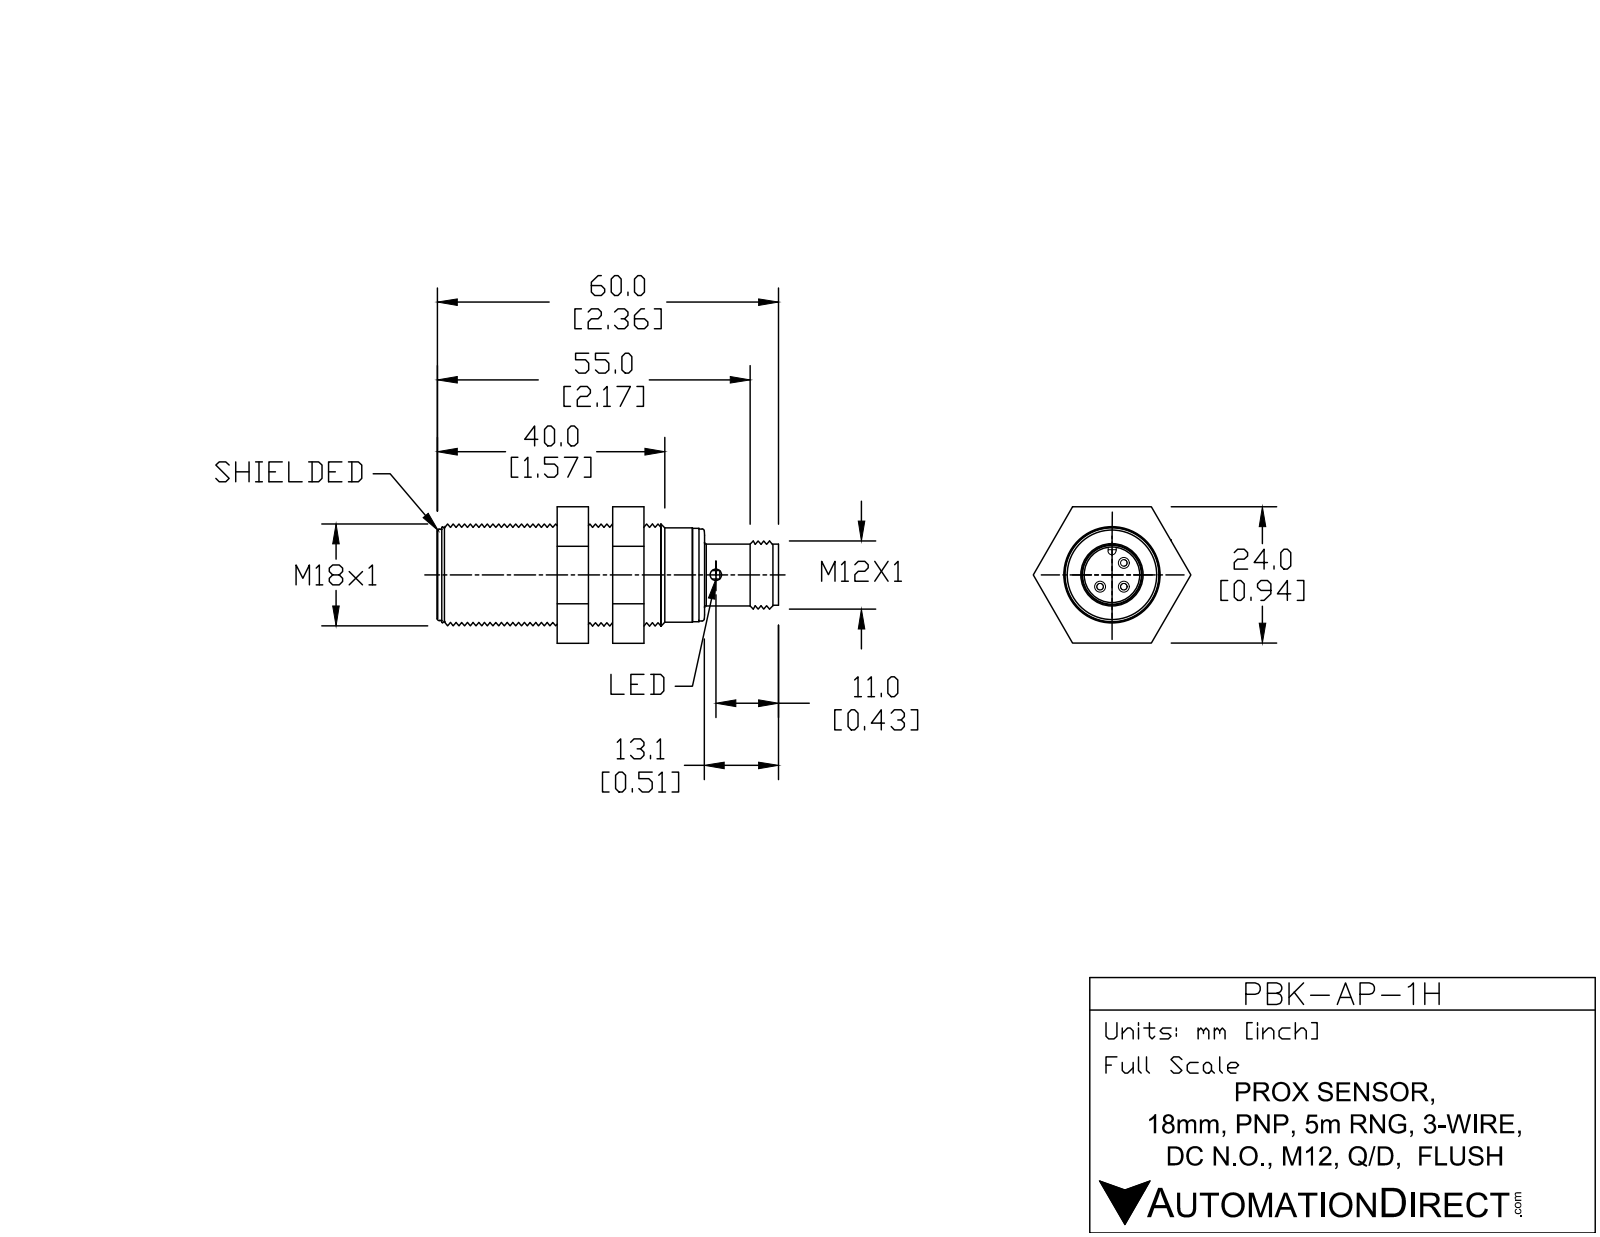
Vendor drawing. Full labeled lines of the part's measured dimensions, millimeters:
Part name (STEP PRODUCT): PBK-AP-1H
STEP written by: SolidWorks 2011 (AUTOMOTIVE_DESIGN)
Units: millimetres
Bodies: 8 solids, 67 faces (38 planar, 18 cylindrical, 11 other)
Overall size (bounding box): 60 × 27.69 × 24.57
Volume: 14 746 mm³ · Surface area: 6 972 mm²
Round holes (diameter × count): ⌀1.25 ×1, ⌀8.5 ×1, ⌀10.5 ×1, ⌀17 ×1
Round bosses / shafts (diameter × count): ⌀1 ×3, ⌀18 ×1, ⌀16.8 ×1, ⌀16.6 ×1, ⌀16.15 ×1, ⌀16 ×1, ⌀12 ×1, ⌀10.9 ×1
Main face-to-face distances: 4.5, 10, 24, 27.75, 32.25, 0.75, 27, 17, 14.5, 31.5
